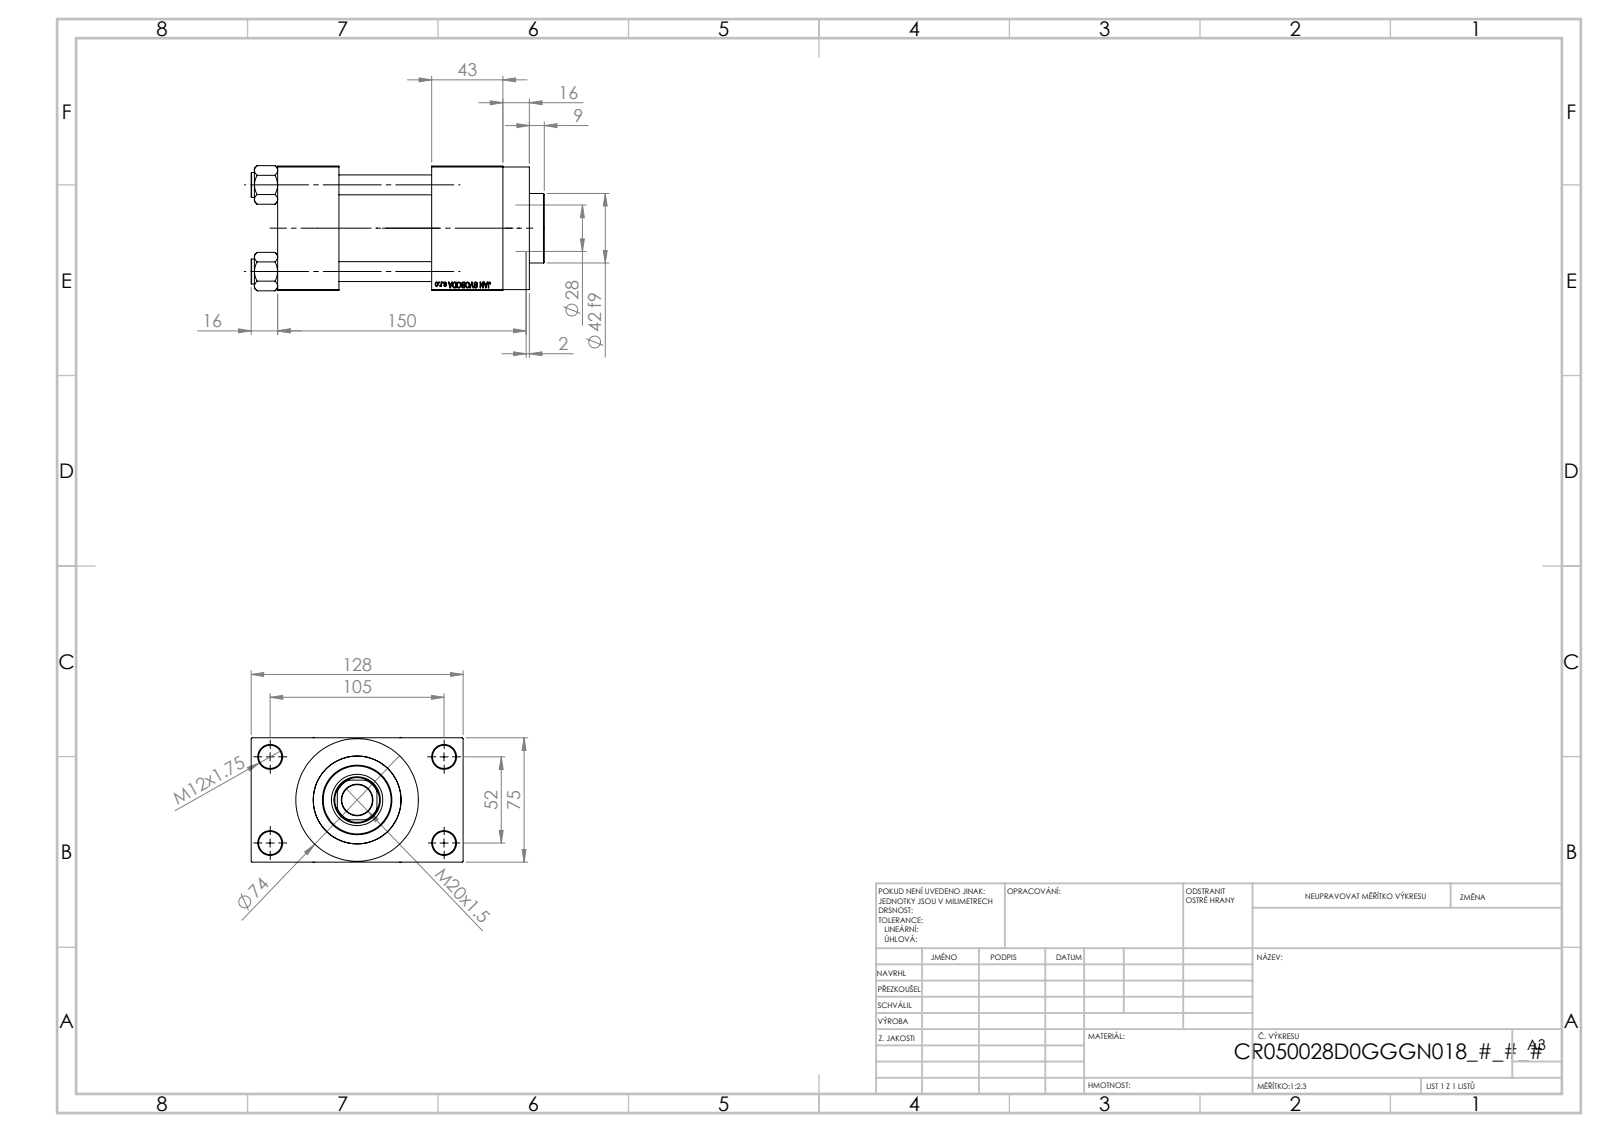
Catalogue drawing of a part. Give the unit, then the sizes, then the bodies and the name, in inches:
Units: inches
Overall size (bounding box): 6.969 × 5.039 × 2.974
Round holes (diameter × count): ⌀0.472 ×4, ⌀0.551 ×4, ⌀0.276 ×2, ⌀0.825 ×2, ⌀1.181 ×2, ⌀0.728 ×1, ⌀1.102 ×1, ⌀1.22 ×1, ⌀1.614 ×1, ⌀1.969 ×1, ⌀2.087 ×1
Round bosses / shafts (diameter × count): ⌀0.591 ×4, ⌀2.913 ×1, ⌀2.205 ×1, ⌀1.654 ×1
Partial cylindrical surfaces — rounded edges, fillets, slot ends (radius × count): R0.531 ×1
Main face-to-face distances: 2.953, 2.205, 1.457, 3.661, 1.043, 3.996, 5.354, 3.898, 1.693, 0.63
Hole centre spacings: 1.037, 1.456, 2.059, 2.3, 2.307, 3.096, 3.715, 2.047
Volume: 47.64 in³ · Surface area: 255.1 in²
Bodies: 11 solids, 1104 faces (497 planar, 89 cylindrical, 518 other)
Part name (STEP PRODUCT): NUT_M5_D; V215CR_D_TYCINKA; V215CR_D_Body; V215_VC_A (+1 more)
STEP written by: SolidWorks 2019 (CONFIG_CONTROL_DESIGN)
